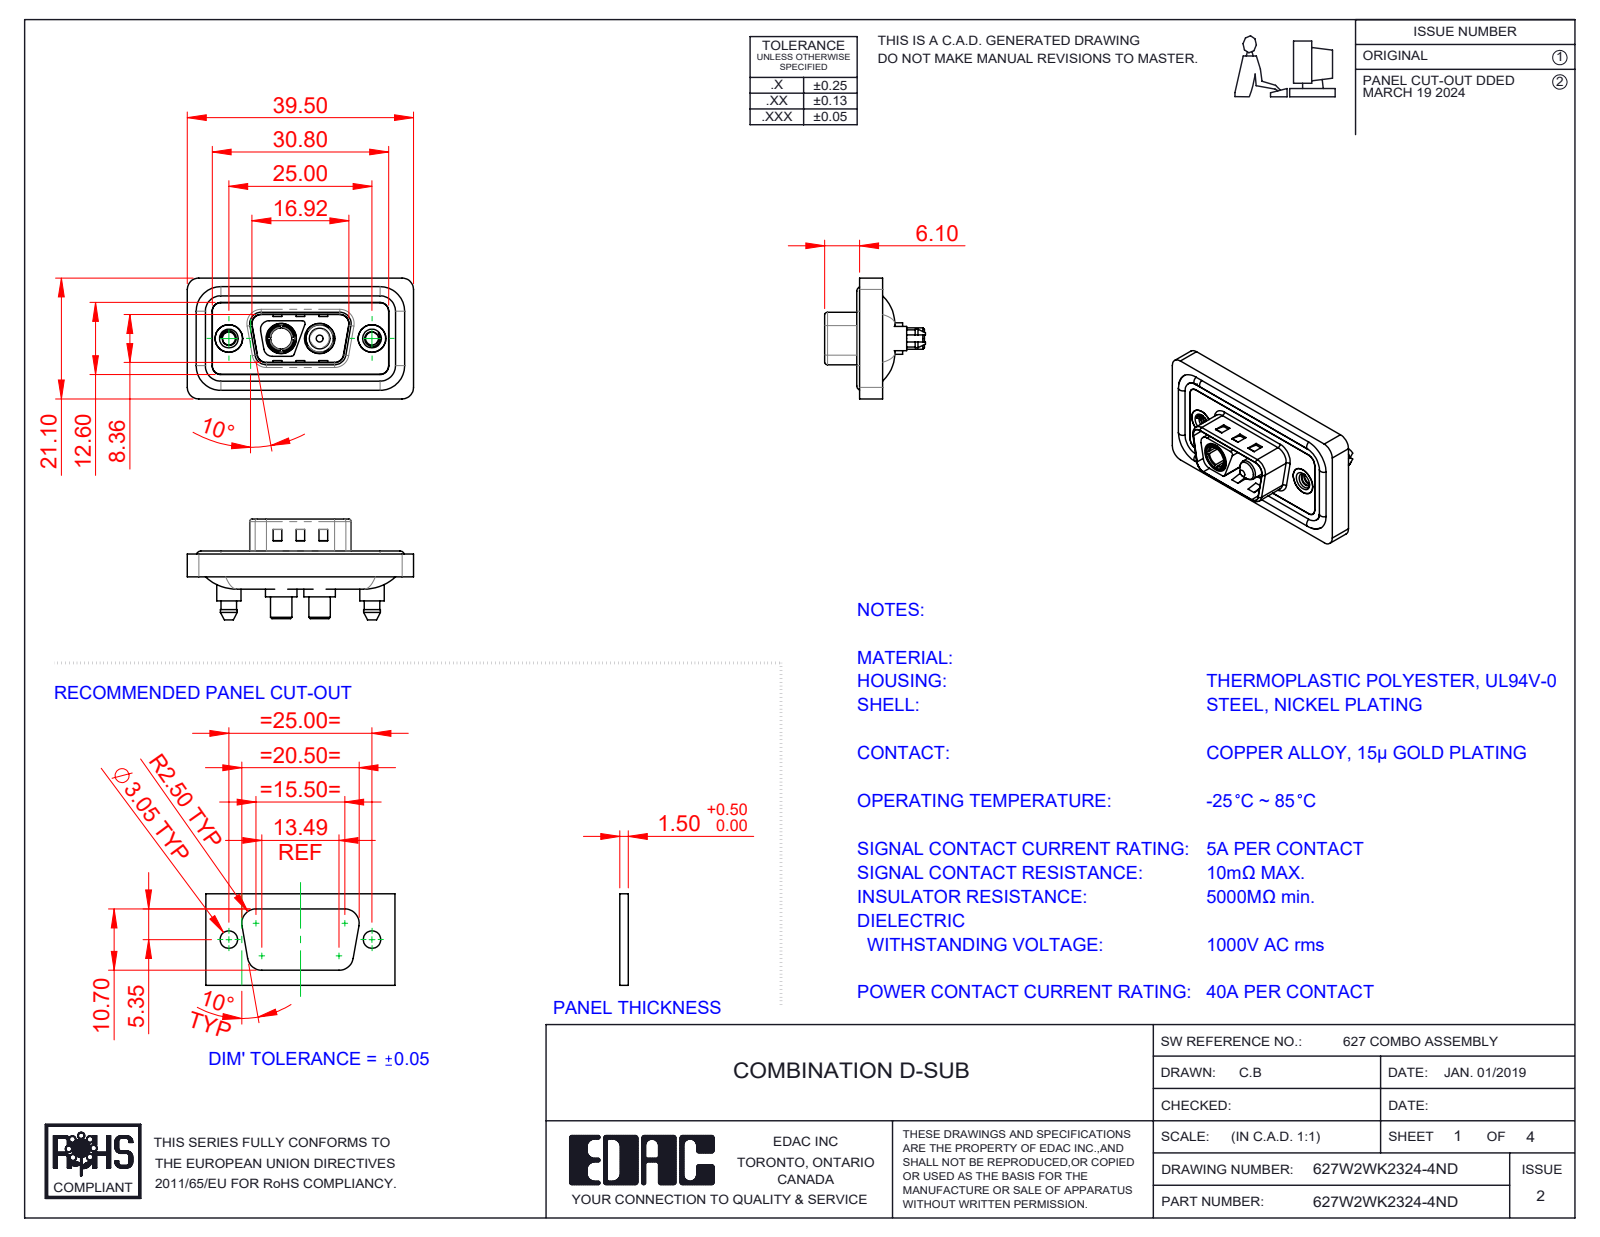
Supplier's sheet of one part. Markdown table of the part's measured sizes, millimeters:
| quantity | value |
| --- | --- |
| part name | 627Combo Shell Rear_09 Contacts; 627Combo Shell Front_09 Contacts; 627W2WK2324-4ND; 627Combo Waterproof Housing_09 Contacts (+5 more) |
| STEP written by | SolidWorks 2023 (CONFIG_CONTROL_DESIGN) |
| units | millimeters |
| bodies | 11 solids, 592 faces (205 planar, 267 cylindrical, 120 other) |
| overall size | 39.5 × 21.1 × 17.6 |
| volume | 4 726 mm³ |
| surface area | 7 700 mm² |
| round holes (diameter × count) | 2.26 × 2, 4 × 2, 4.8 × 2, 4.85 × 2, 5 × 2, 5.3 × 2, 3.7 × 1 |
| round bosses / shafts (diameter × count) | 1.6 × 4, 5.5 × 2, 5.4 × 2, 5.2 × 2, 4.9 × 2, 4.75 × 2, 4.25 × 2, 3.75 × 2 |
| partial cylindrical surfaces (radius × count) | 1.5 × 26, 2 × 18, 0.5 × 10, 1.6 × 10, 0.25 × 4, 0.6 × 4, 0.65 × 4, 0.9 × 4 |
| main face-to-face distances | 0.4, 1.1, 2.9, 3.1, 0.5, 1.6, 1.5, 4, 1.8, 3.2 |
| hole center spacings | 9.14, 15.86, 6.72, 25 |
